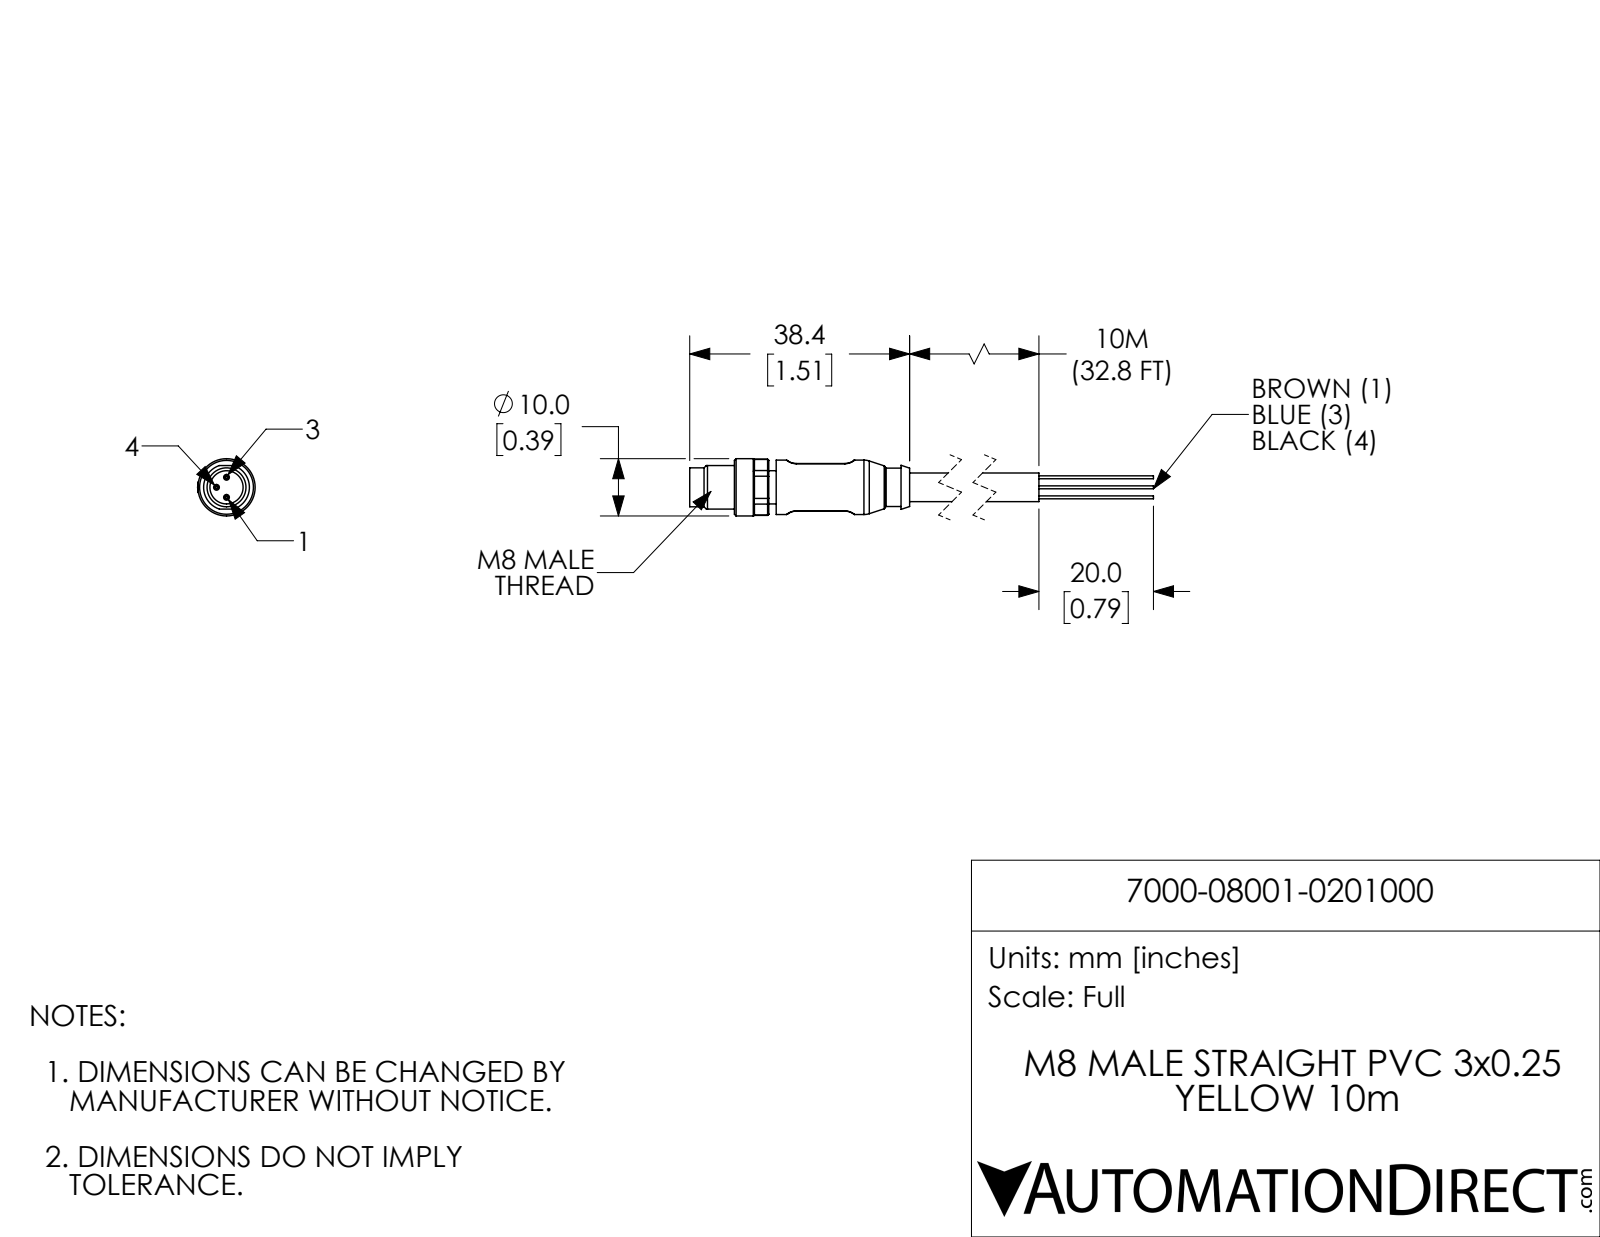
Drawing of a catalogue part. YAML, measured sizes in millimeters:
part_name: "7000-08001-0201000"
step_written_by: "SolidWorks 2017 (AUTOMOTIVE_DESIGN)"
units: millimeters
bodies: {solids: 4, faces: 119, planar: 41, cylindrical: 44, other: 34}
overall_size: [78.4, 10.05, 10]
volume: 2535
surface_area: 1801
round_holes:
  - {diameter: 5.8, count: 1}
round_bosses_or_shafts:
  - {diameter: 1, count: 3}
  - {diameter: 0.51, count: 3}
  - {diameter: 10, count: 1}
  - {diameter: 9.5, count: 1}
  - {diameter: 8, count: 1}
  - {diameter: 6.8, count: 1}
  - {diameter: 6.7, count: 1}
  - {diameter: 5, count: 1}
partial_cylinders:
  - {radius: 0.2, count: 4}
  - {radius: 2.5, count: 4}
  - {radius: 4.9, count: 1}
  - {radius: 5.05, count: 1}
face_to_face_distances: [8.3, 1.3, 9, 0.35, 7.95, 8.8, 10.1, 53.4, 44.6, 43.3]
